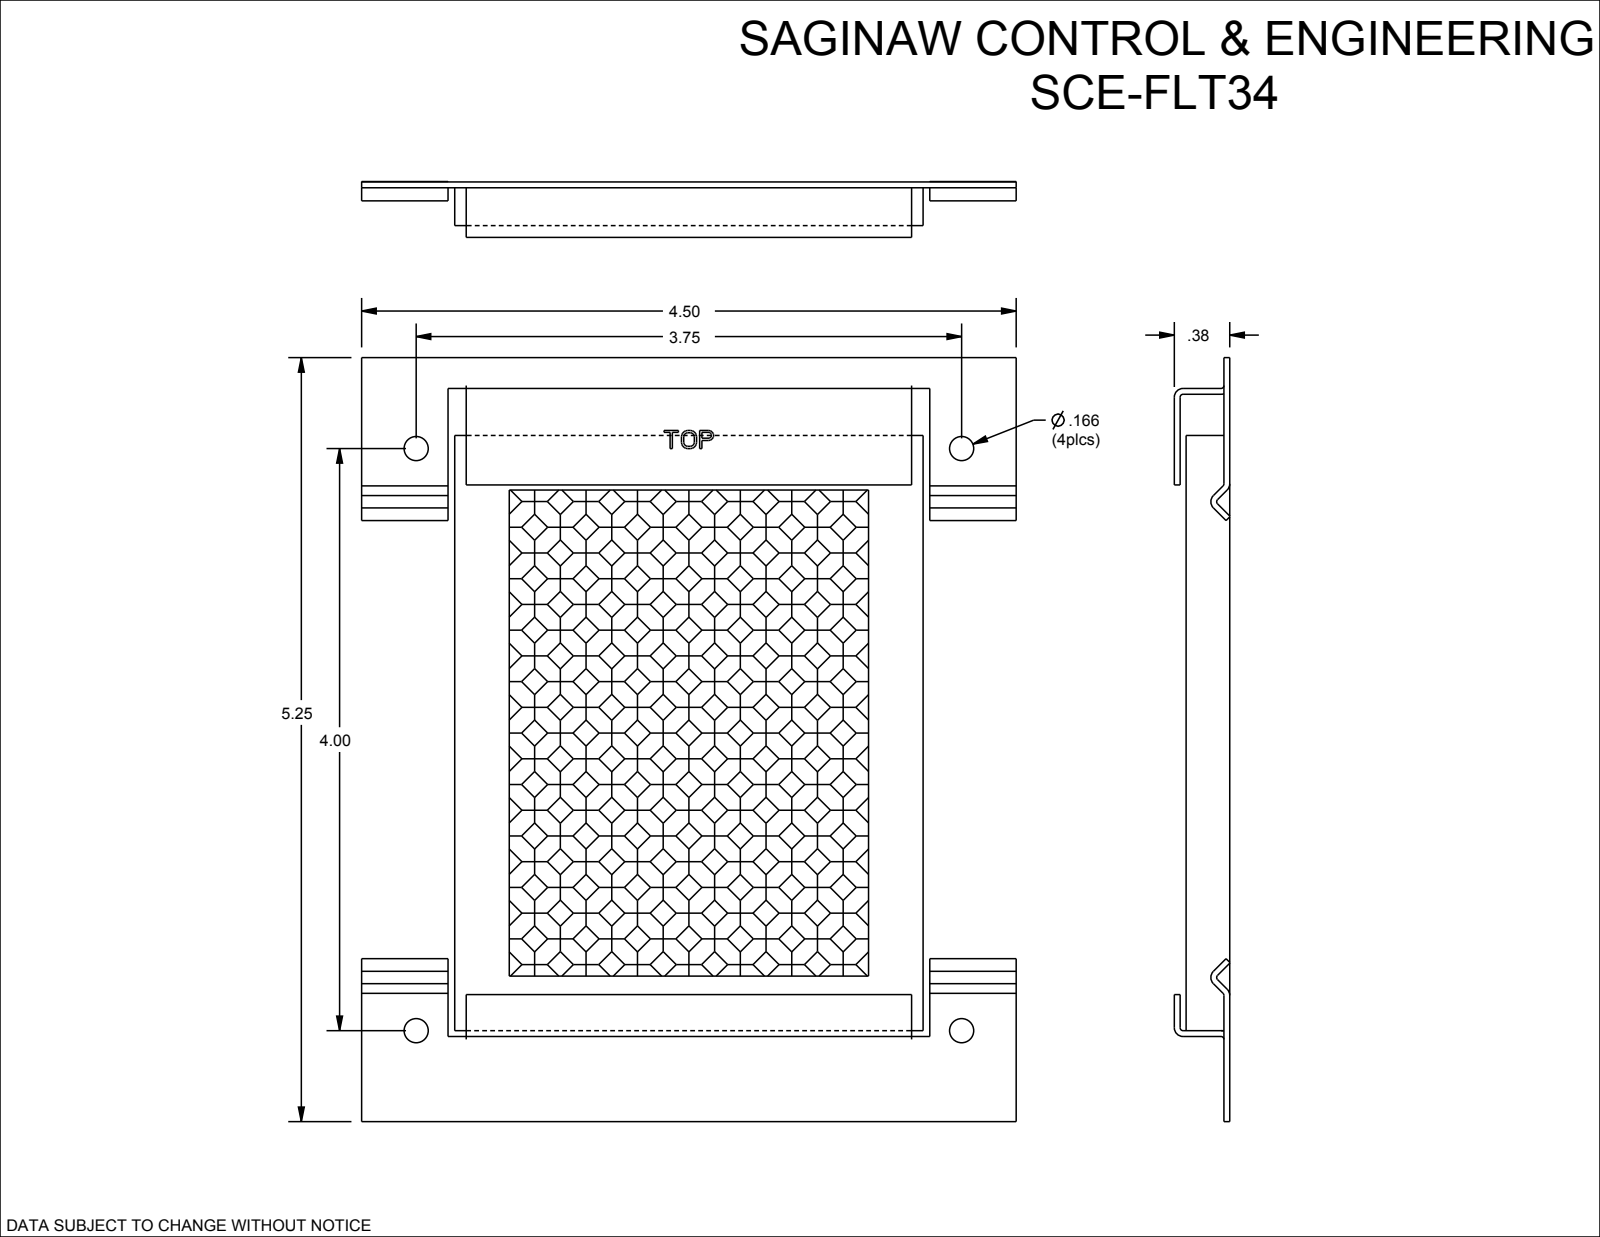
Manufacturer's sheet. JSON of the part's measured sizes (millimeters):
{"part_name": "SCE-FLT34", "step_written_by": "SolidWorks 2019 (CONFIG_CONTROL_DESIGN)", "units": "millimeters", "bodies": {"solids": 3, "faces": 944, "planar": 356, "cylindrical": 588, "other": 0}, "overall_size": [133.4, 114.3, 9.8], "volume_mm3": 41970, "surface_area_mm2": 38020, "round_holes": [[4.2, 4]], "round_bosses_or_shafts": [[3.2, 21], [3.2, 11]], "partial_cylinders_radius": [[0.5, 8], [1.5, 8]], "face_to_face_distances": [1, 7.6, 6.6, 1, 9.5, 2.1, 8.7, 9.7, 1, 7.6], "hole_center_spacings": [95.3, 101.6, 139.3]}
